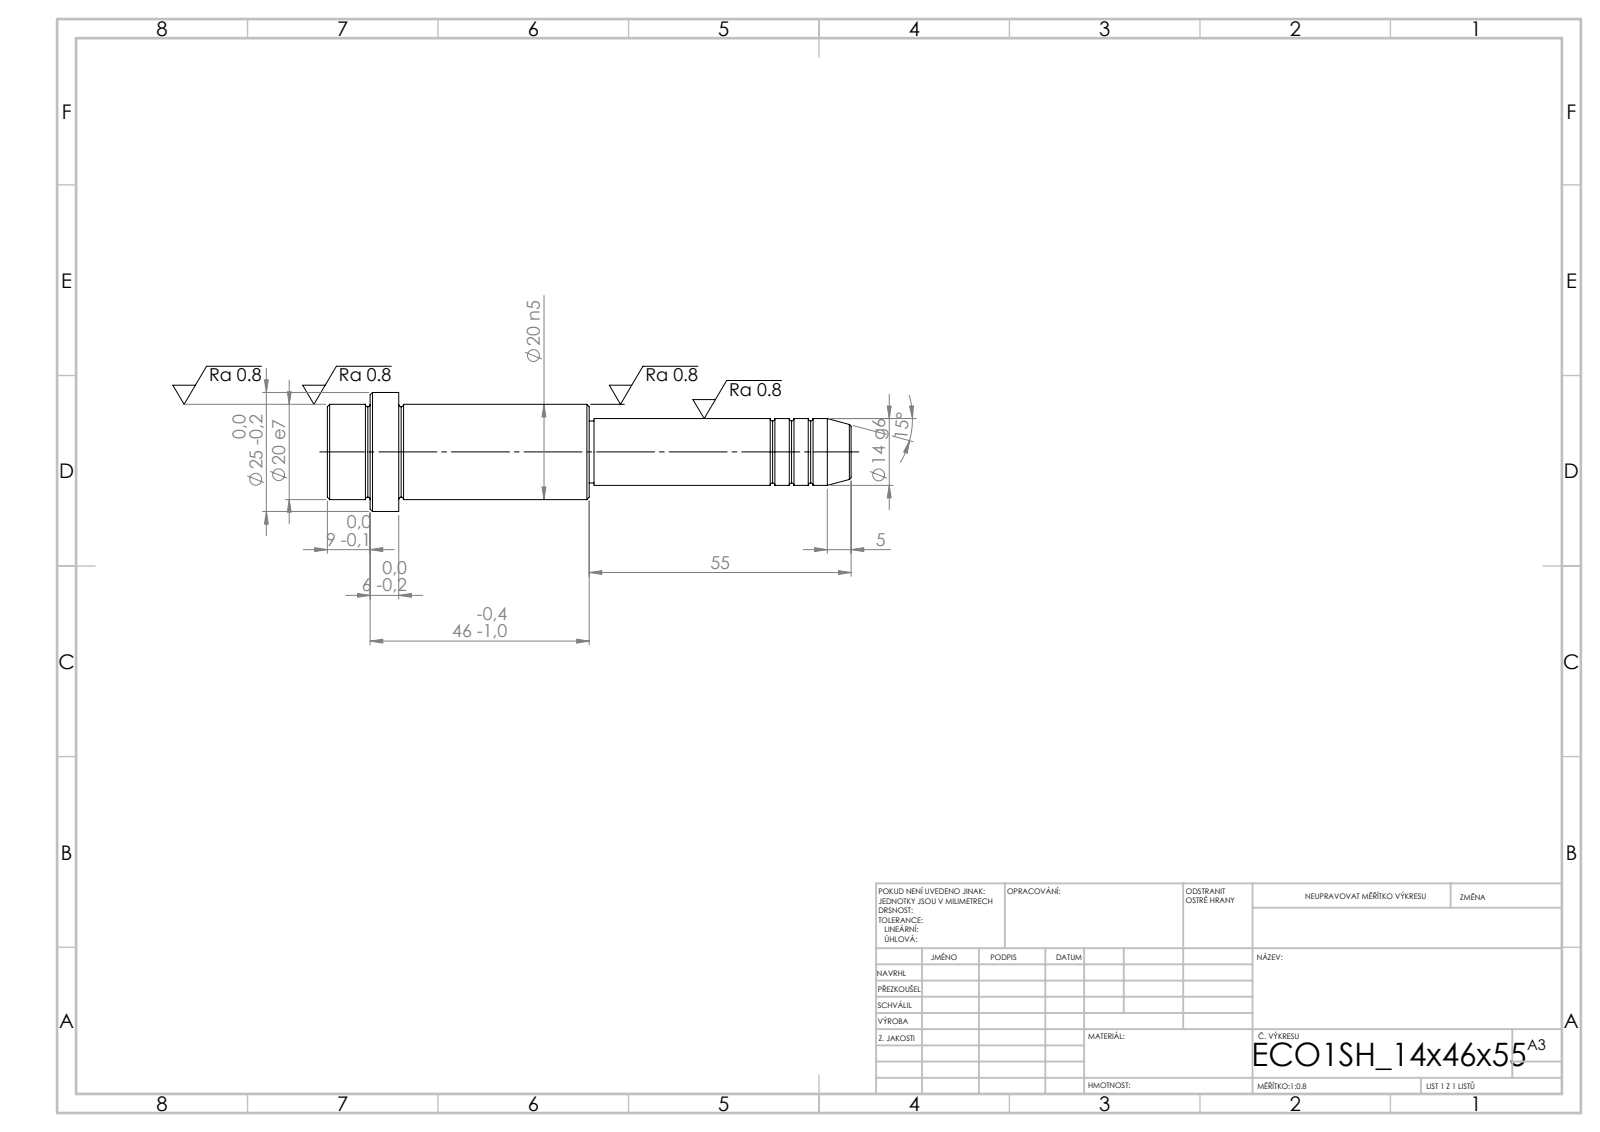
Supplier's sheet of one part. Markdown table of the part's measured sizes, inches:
| quantity | value |
| --- | --- |
| STEP written by | SolidWorks 2019 (CONFIG_CONTROL_DESIGN) |
| units | inches |
| bodies | 1 solid, 52 faces (6 planar, 16 cylindrical, 30 other) |
| overall size | 4.331 × 0.984 × 0.984 |
| volume | 1.618 in³ |
| surface area | 10.83 in² |
| round bosses / shafts (diameter × count) | 0.984 × 1, 0.787 × 1, 0.551 × 1, 0.512 × 1 |
| main face-to-face distances | 2.165, 0.591, 1.575, 1.811, 0.236, 0.354, 3.74, 3.976, 4.331, 2.126 |
